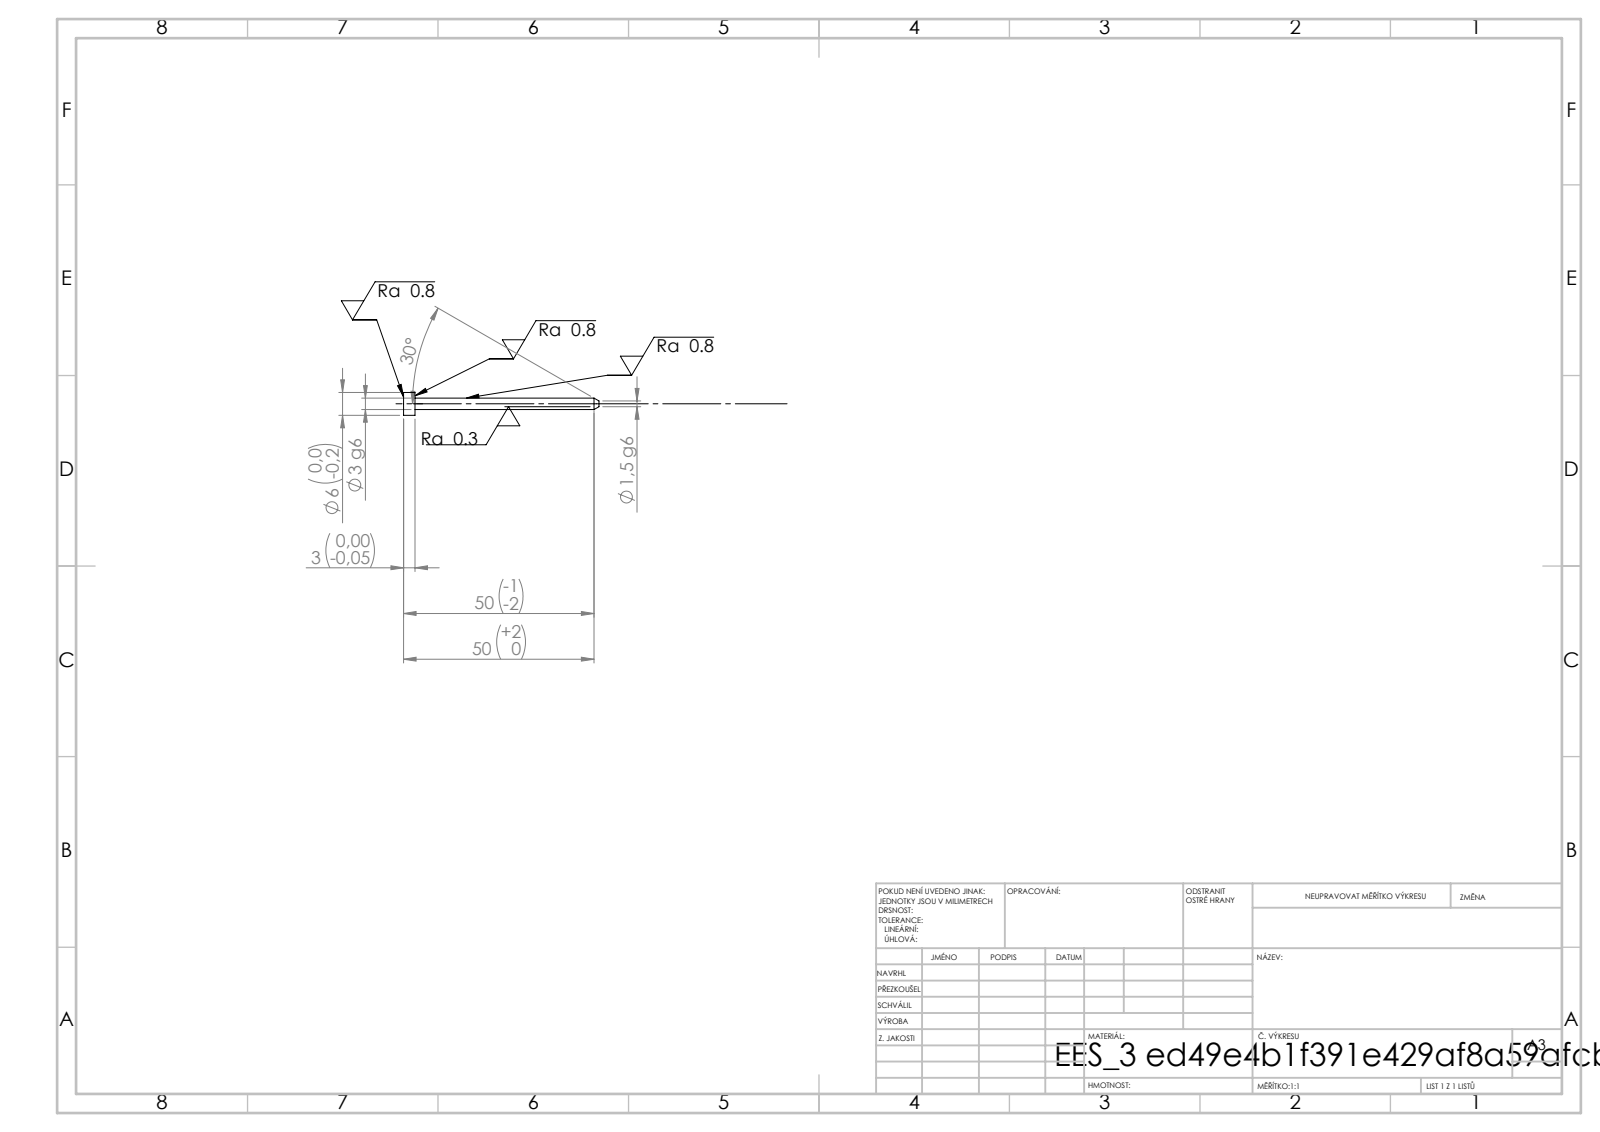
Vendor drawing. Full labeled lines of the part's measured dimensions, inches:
STEP written by: SolidWorks 2019 (CONFIG_CONTROL_DESIGN)
Units: inches
Bodies: 1 solid, 11 faces (3 planar, 6 cylindrical, 2 other)
Overall size (bounding box): 2.02 × 0.236 × 0.236
Volume: 0.026 in³ · Surface area: 0.879 in²
Round holes (diameter × count): ⌀0.059 ×1
Round bosses / shafts (diameter × count): ⌀0.236 ×1, ⌀0.118 ×1
Main face-to-face distances: 0.118, 1.85, 1.969
